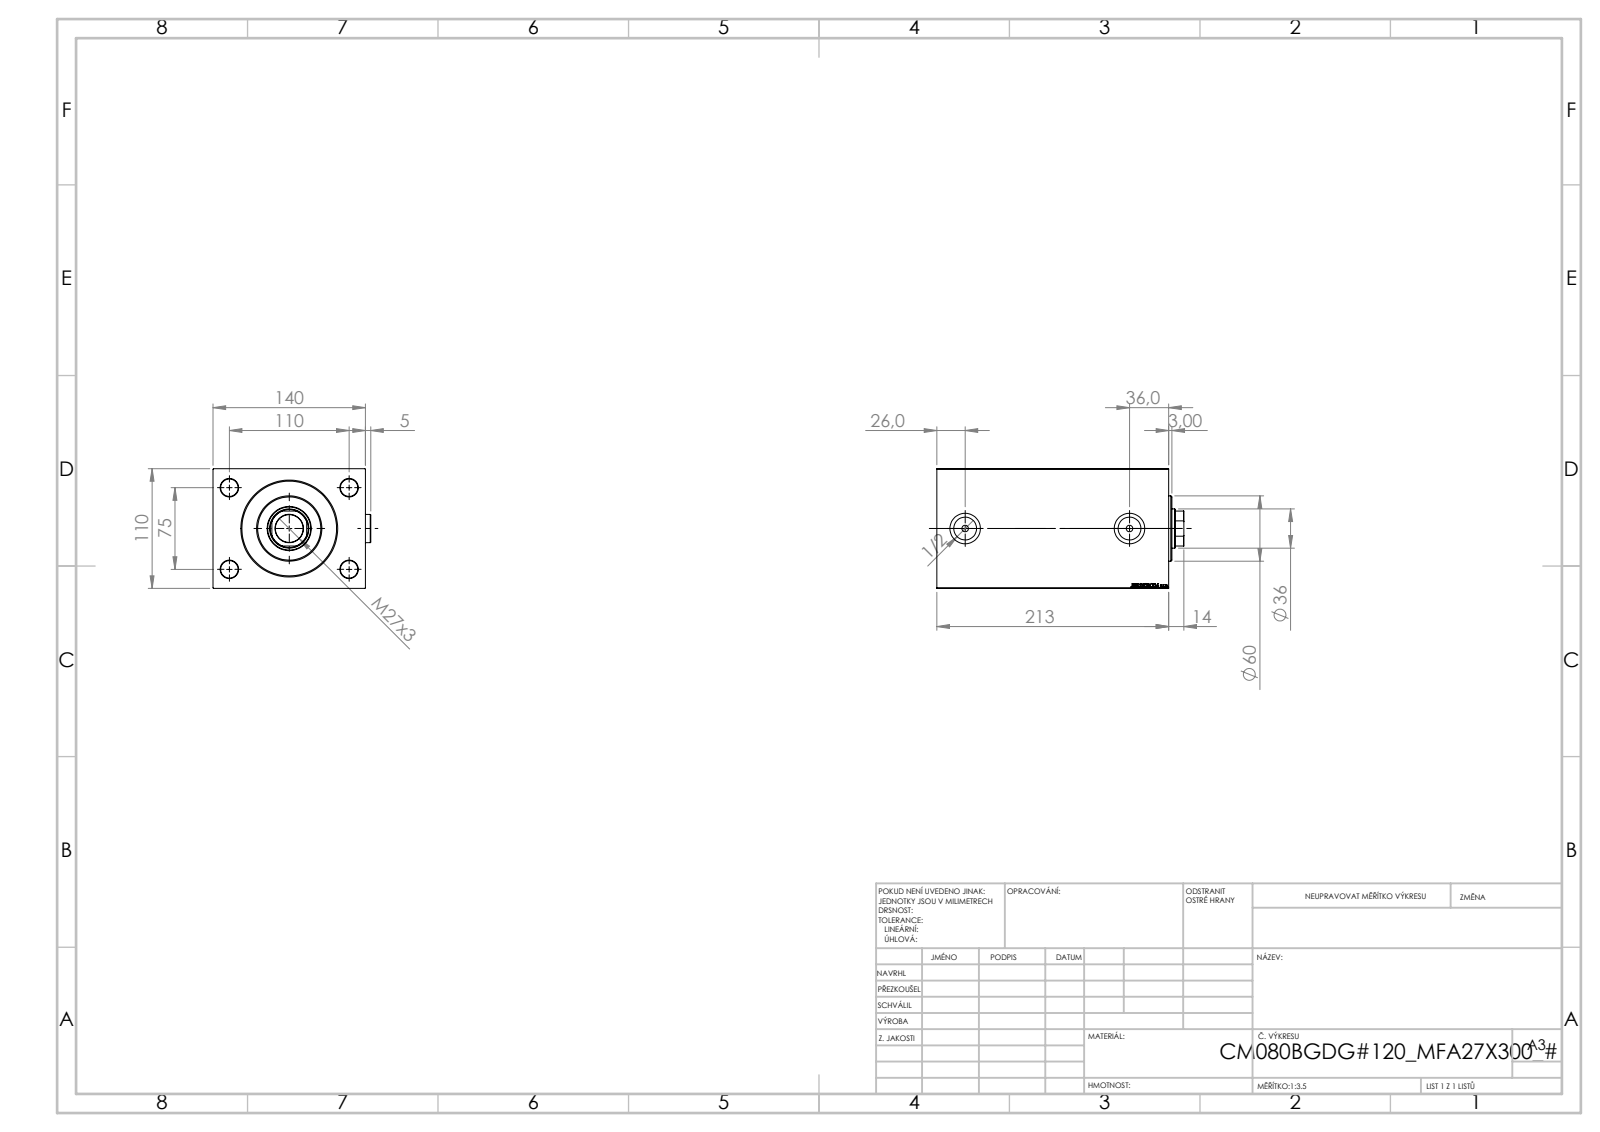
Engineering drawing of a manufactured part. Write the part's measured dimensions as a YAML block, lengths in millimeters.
part_name: "Zatka_OIL_PORT; V450CM_B_VCP; V450CM_VC_B; V450CM_B_Body"
step_written_by: "SolidWorks 2019 (CONFIG_CONTROL_DESIGN)"
units: millimeters
bodies: {solids: 5, faces: 938, planar: 436, cylindrical: 72, other: 430}
overall_size: [227, 144.9, 110]
volume: 2733000
surface_area: 265107
round_holes:
  - {diameter: 16, count: 4}
  - {diameter: 6, count: 2}
  - {diameter: 20.96, count: 2}
  - {diameter: 28, count: 2}
  - {diameter: 25.5, count: 1}
  - {diameter: 36, count: 1}
  - {diameter: 39.5, count: 1}
  - {diameter: 40.5, count: 1}
  - {diameter: 80, count: 1}
  - {diameter: 82, count: 1}
  - {diameter: 87, count: 1}
round_bosses_or_shafts:
  - {diameter: 26, count: 2}
  - {diameter: 60, count: 1}
partial_cylinders:
  - {radius: 17.5, count: 1}
face_to_face_distances: [110, 140, 213, 192, 21, 14, 178, 199, 134, 120]
hole_center_spacings: [66.57, 75, 110, 133.14, 151]
